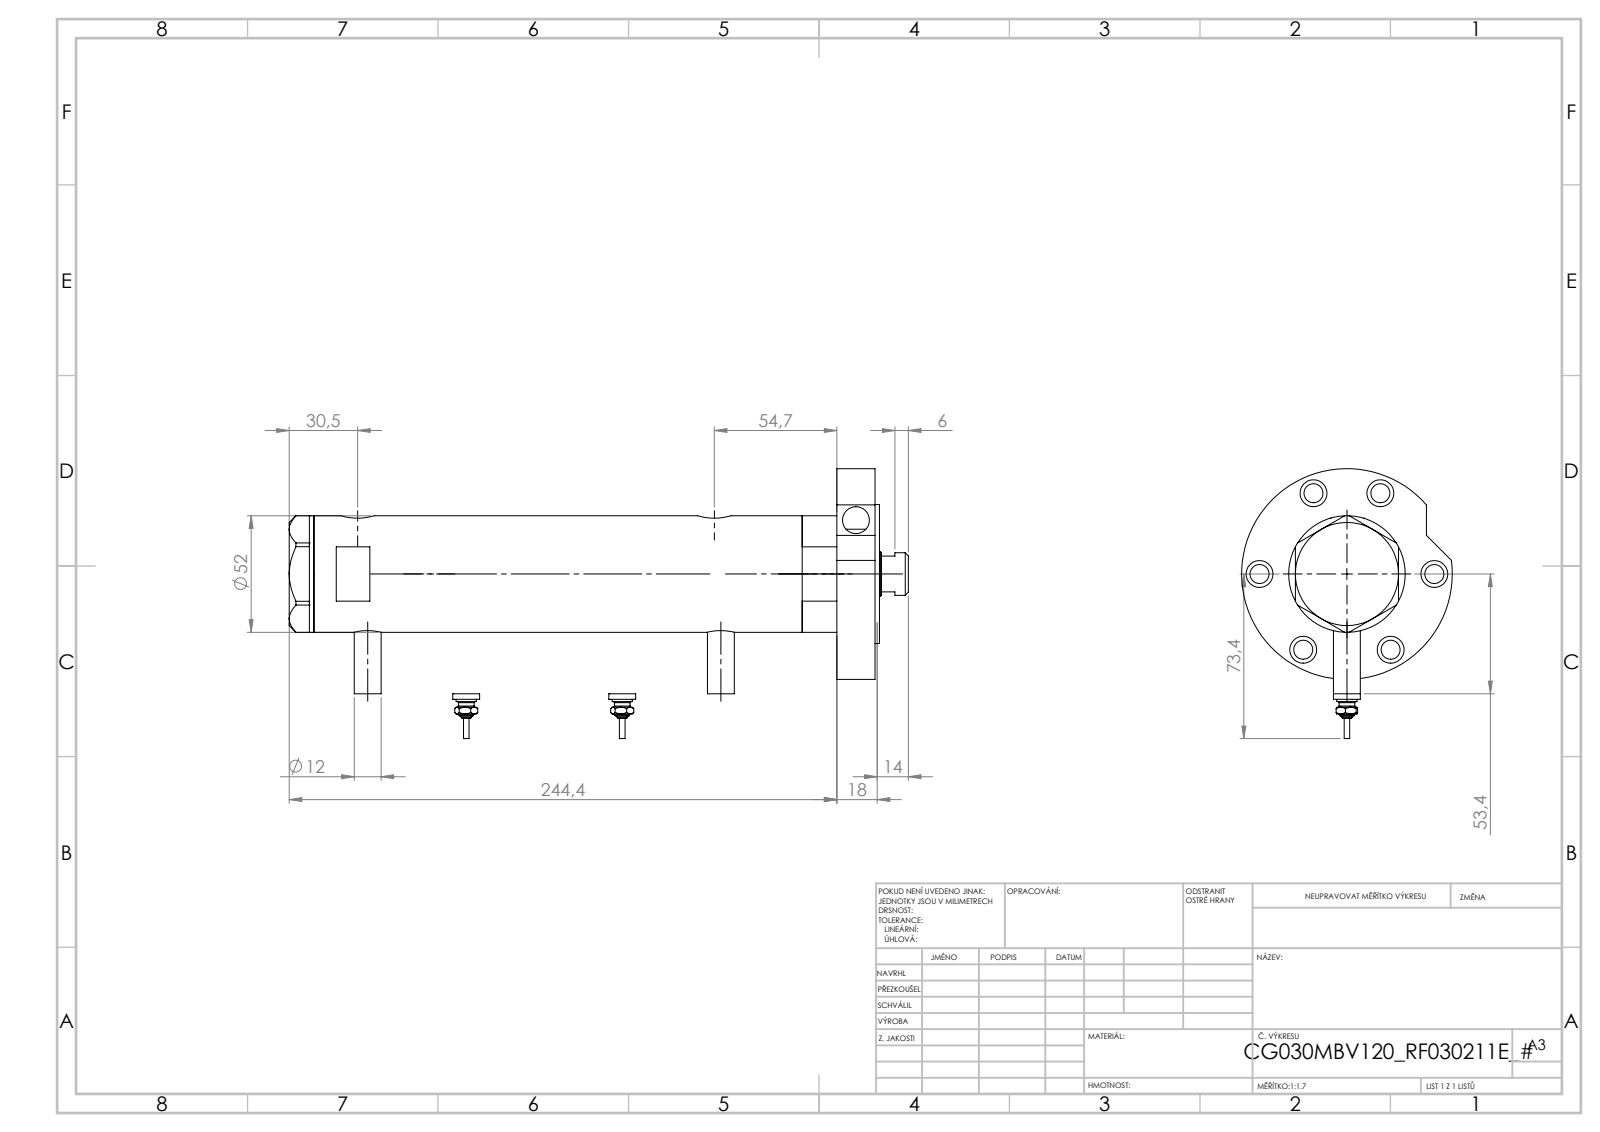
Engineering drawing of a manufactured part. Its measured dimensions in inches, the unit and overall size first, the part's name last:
Units: inches
Overall size (bounding box): 10.878 × 4.74 × 3.701
Round holes (diameter × count): ⌀0.472 ×7, ⌀0.335 ×6, ⌀0.383 ×2, ⌀0.492 ×2, ⌀0.591 ×2, ⌀0.256 ×1, ⌀0.787 ×1, ⌀0.846 ×1, ⌀1.181 ×1, ⌀1.299 ×1, ⌀1.575 ×1, ⌀1.732 ×1
Round bosses / shafts (diameter × count): ⌀0.472 ×4, ⌀0.354 ×2, ⌀0.276 ×2, ⌀0.177 ×2, ⌀0.098 ×2, ⌀3.701 ×1, ⌀2.441 ×1, ⌀2.047 ×1
Main face-to-face distances: 0.669, 9.189, 9.858, 0.079, 9.937, 7.146, 2.043, 2.713, 2.791, 0.748
Hole centre spacings: 1.535, 1.706, 2.553, 2.659, 2.754, 3.064, 0.114, 0.177
Volume: 35.39 in³ · Surface area: 205.7 in²
Bodies: 7 solids, 270 faces (104 planar, 102 cylindrical, 64 other)
Part name (STEP PRODUCT): V270CG_RF211E; V270CG_FRONT; V270CG_MIDDLE; Switch (+2 more)
STEP written by: SolidWorks 2019 (CONFIG_CONTROL_DESIGN)
